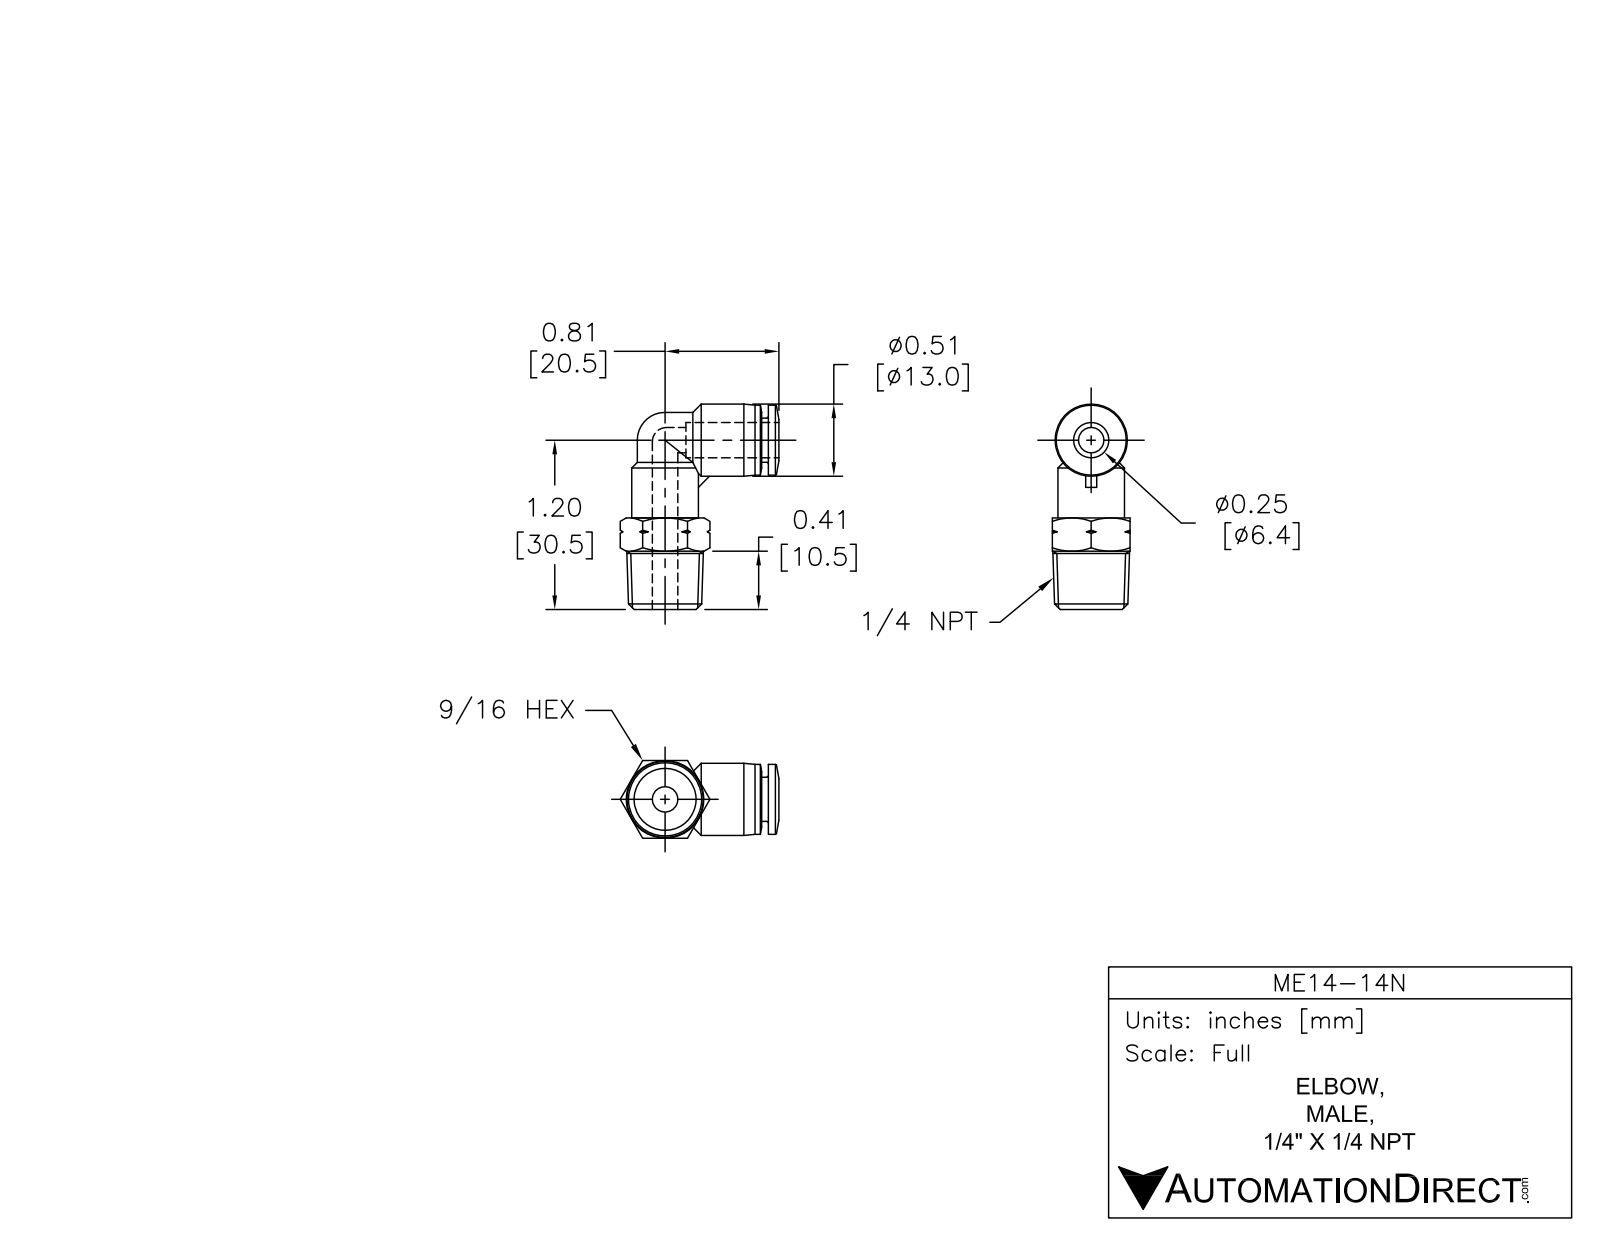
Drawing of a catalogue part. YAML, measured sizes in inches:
part_name: "ME14-14N"
step_written_by: "SolidWorks 2015 (AUTOMOTIVE_DESIGN)"
units: inches
bodies: {solids: 1, faces: 88, planar: 15, cylindrical: 20, other: 53}
overall_size: [1.457, 1.125, 0.551]
volume: 0.307
surface_area: 4.968
round_holes:
  - {diameter: 0.177, count: 2}
  - {diameter: 0.258, count: 1}
round_bosses_or_shafts:
  - {diameter: 0.394, count: 2}
  - {diameter: 0.512, count: 1}
  - {diameter: 0.496, count: 1}
  - {diameter: 0.472, count: 1}
  - {diameter: 0.313, count: 1}
face_to_face_distances: [0.551, 0.65, 0.047, 0.539, 0.587, 0.236, 0.315, 0.413, 0.079]
